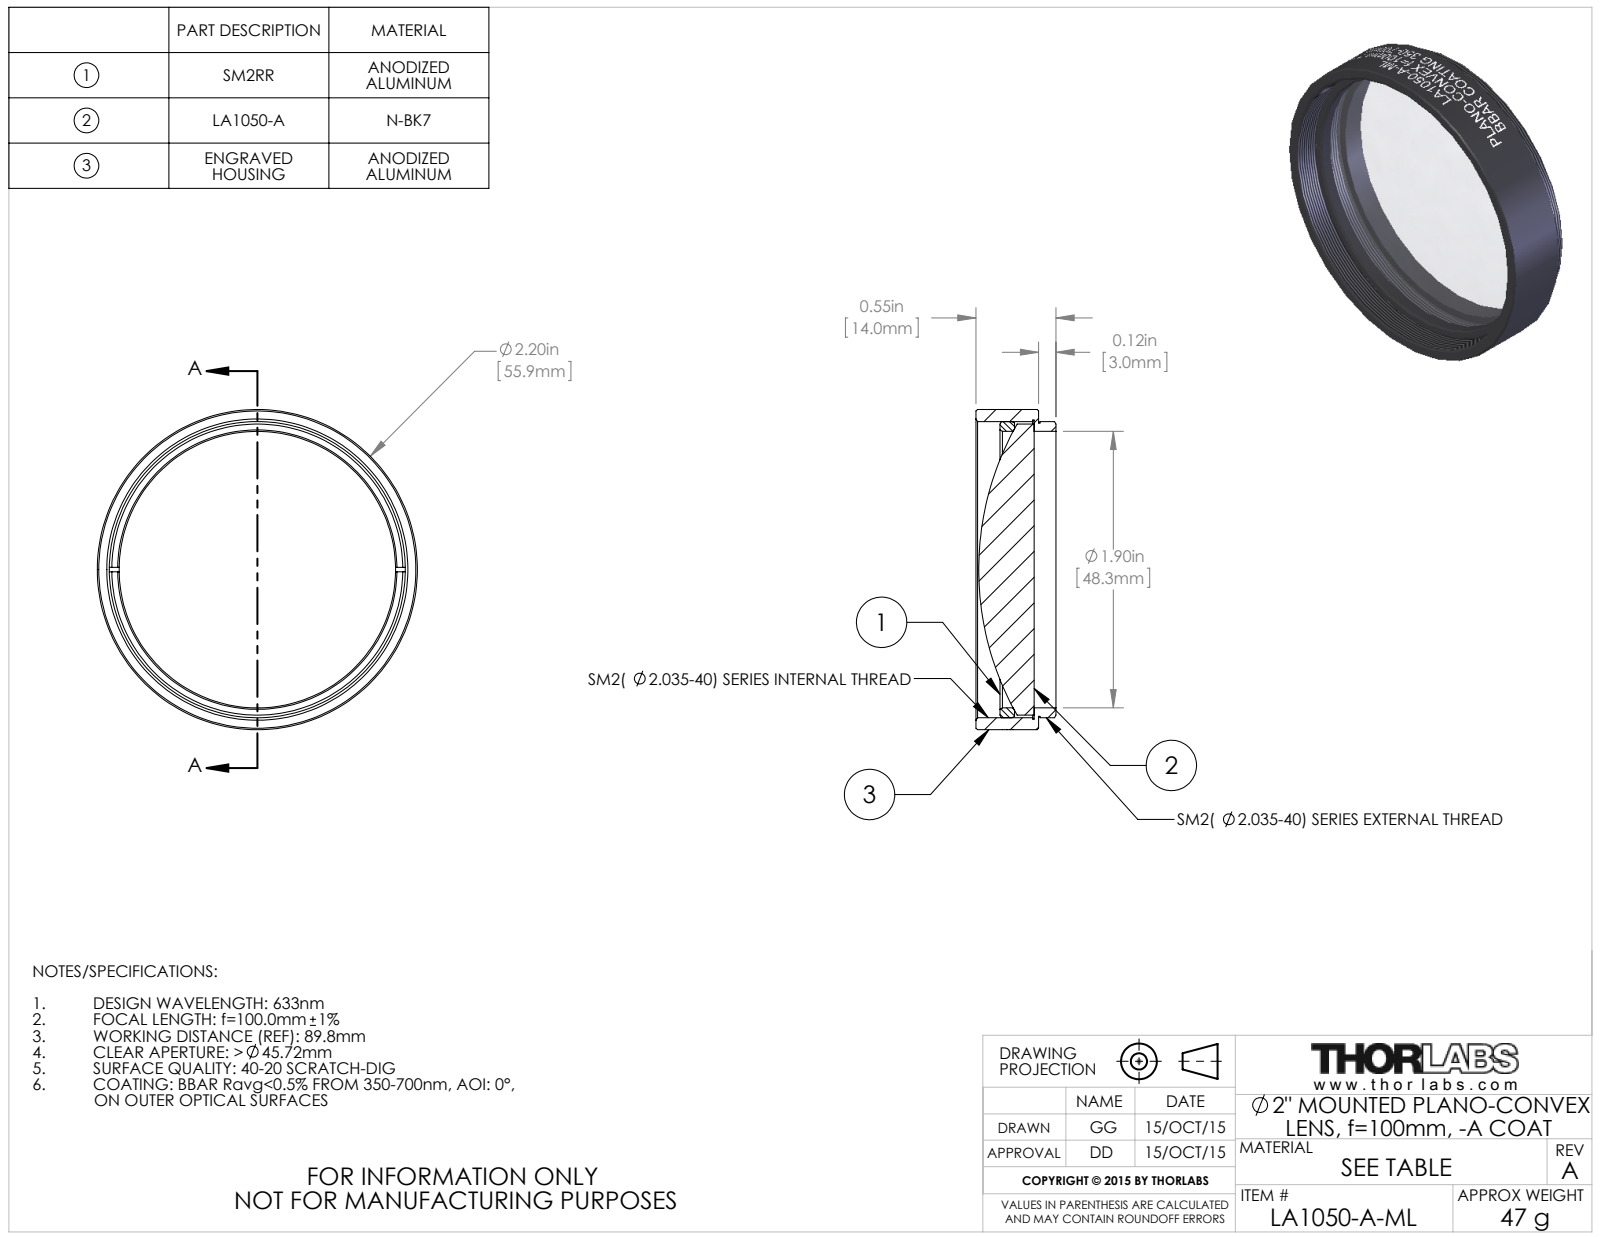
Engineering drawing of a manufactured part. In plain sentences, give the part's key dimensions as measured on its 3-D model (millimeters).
The part is named "TTN039490-E0W". Its 3-D file was written by "SolidWorks 2014 (CONFIG_CONTROL_DESIGN)". It is 3 solids with 143 faces: 16 planar, 107 cylindrical and 20 other. Overall it measures 55.9 by 55.9 by 14 millimeters. Its volume is 18 500 cubic millimeters and its surface area 11 830 square millimeters. Round holes: 1 of diameter 48.3, 1 of diameter 52.2. Round bosses or shafts: 1 of diameter 55.9, 1 of diameter 51.7, 1 of diameter 51.2, 1 of diameter 50.8. The main face-to-face distances are 0.8, 0.8, 10.9, 10.2, 10.2, 3, 3.8, 3.8, 14, 7.3.
